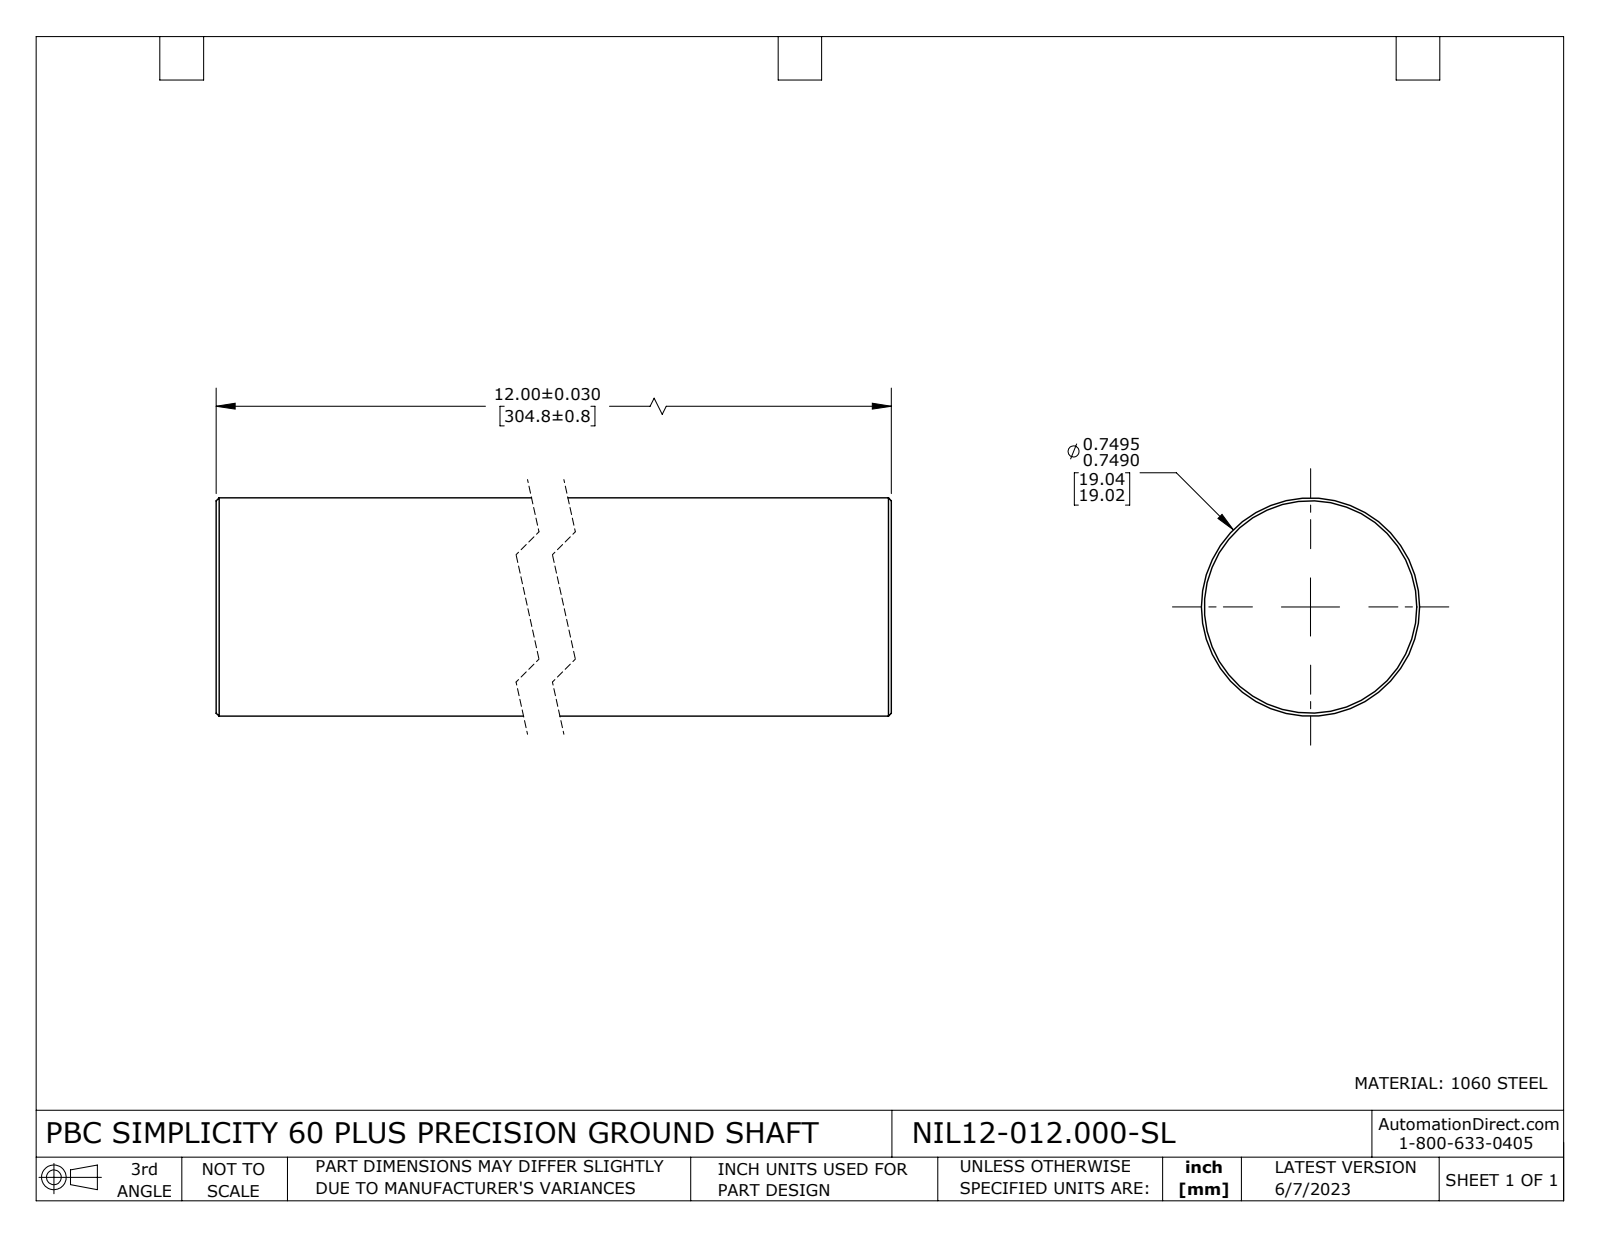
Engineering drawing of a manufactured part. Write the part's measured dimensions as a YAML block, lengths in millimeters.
part_name: "NIL12-012.000-SL"
step_written_by: "SolidWorks 2021 (CONFIG_CONTROL_DESIGN)"
units: millimeters
bodies: {solids: 1, faces: 8, planar: 2, cylindrical: 2, other: 4}
overall_size: [304.8, 19.1, 19.1]
volume: 86870
surface_area: 18790
round_bosses_or_shafts:
  - {diameter: 19.1, count: 1}
face_to_face_distances: [304.8]
